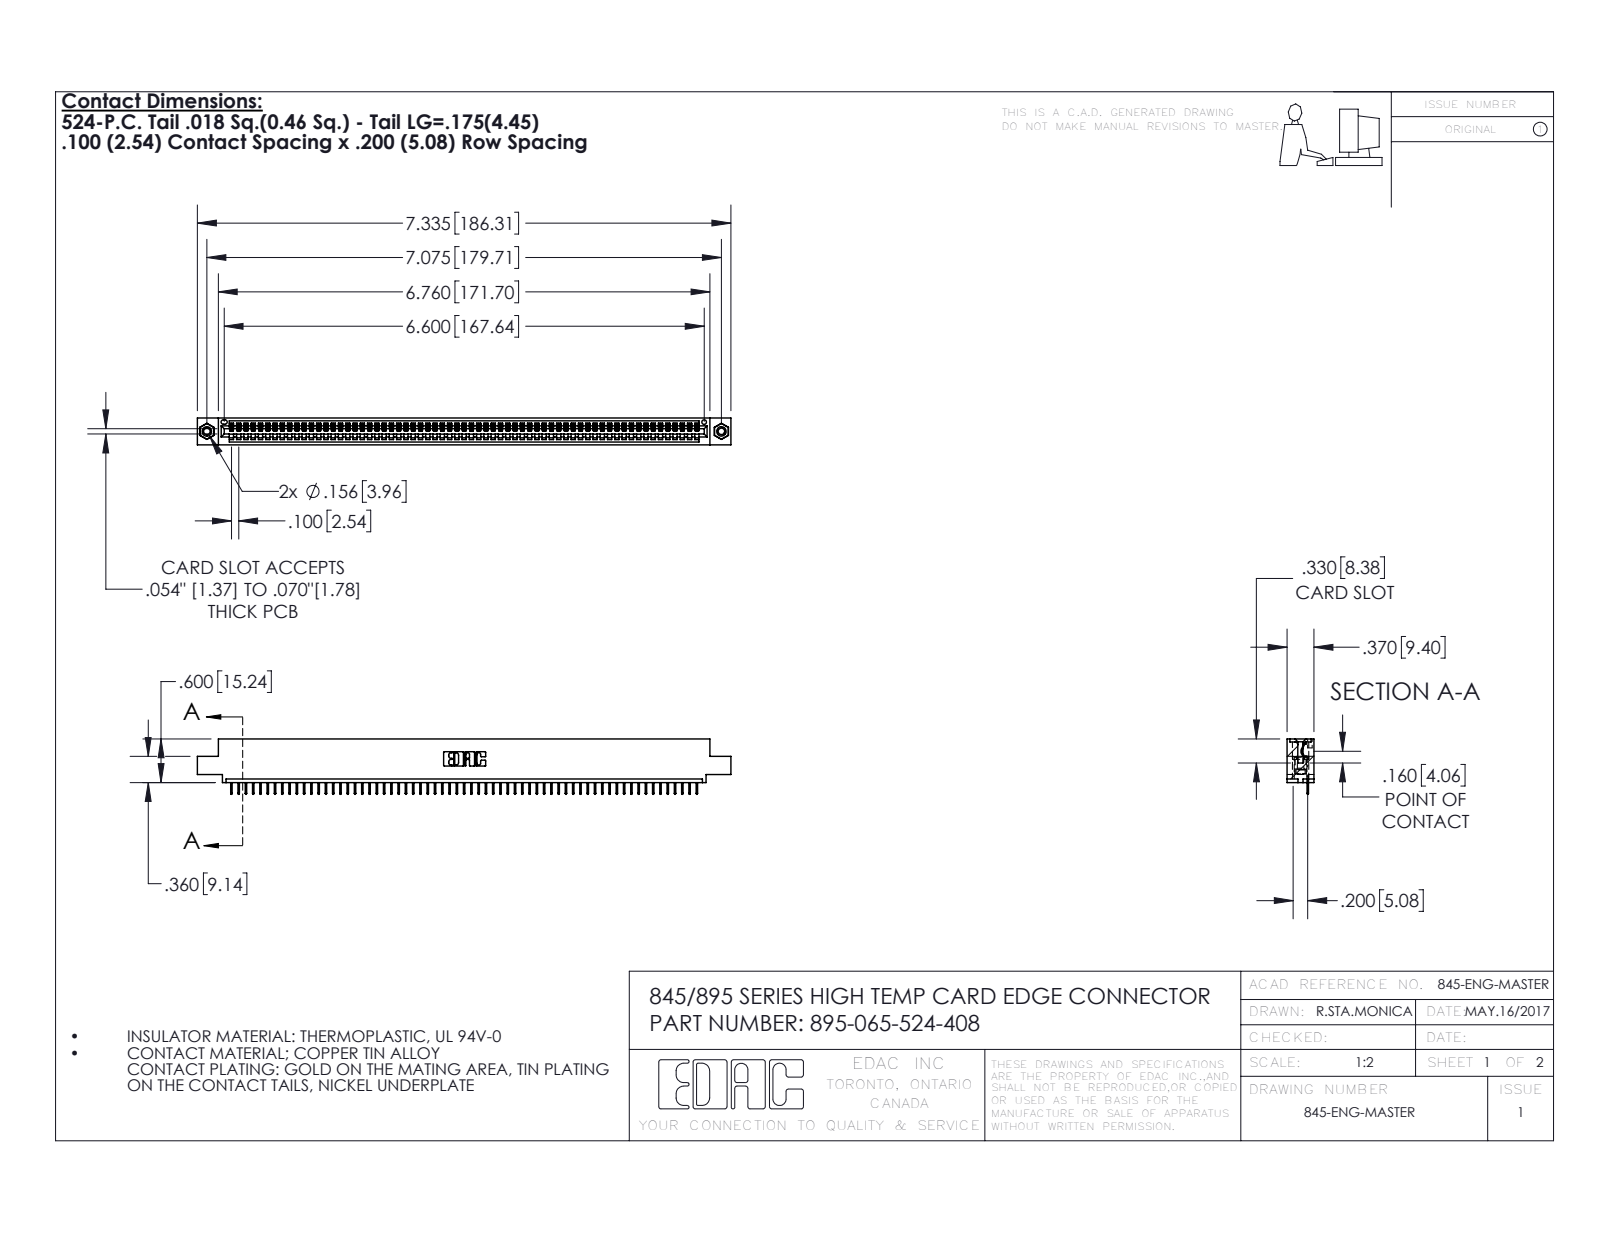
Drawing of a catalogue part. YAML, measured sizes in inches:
part_name: "395-065-524-408; 345-250-001_345-250-003-102; 345 Part_0.110 Offset - 0.156 Dia-TI; 345-292-001_345-293-124"
step_written_by: "SolidWorks 2016 (CONFIG_CONTROL_DESIGN)"
units: inches
bodies: {solids: 68, faces: 4220, planar: 3106, cylindrical: 1098, other: 16}
overall_size: [7.335, 0.762, 0.37]
volume: 1.071
surface_area: 35.51
round_holes:
  - {diameter: 0.089, count: 2}
  - {diameter: 0.125, count: 2}
  - {diameter: 0.156, count: 2}
  - {diameter: 0.064, count: 1}
round_bosses_or_shafts:
  - {diameter: 0.155, count: 2}
partial_cylinders:
  - {radius: 0.006, count: 130}
  - {radius: 0.01, count: 22}
  - {radius: 0.007, count: 6}
  - {radius: 0.031, count: 6}
  - {radius: 0.026, count: 3}
  - {radius: 0.031, count: 2}
  - {radius: 0.04, count: 2}
  - {radius: 0.014, count: 1}
face_to_face_distances: [0.072, 0.298, 0.37, 0.2, 0.098, 0.272, 0.025, 0.225, 0.072, 0.149]
hole_center_spacings: [0.27, 6.839, 7.075]
